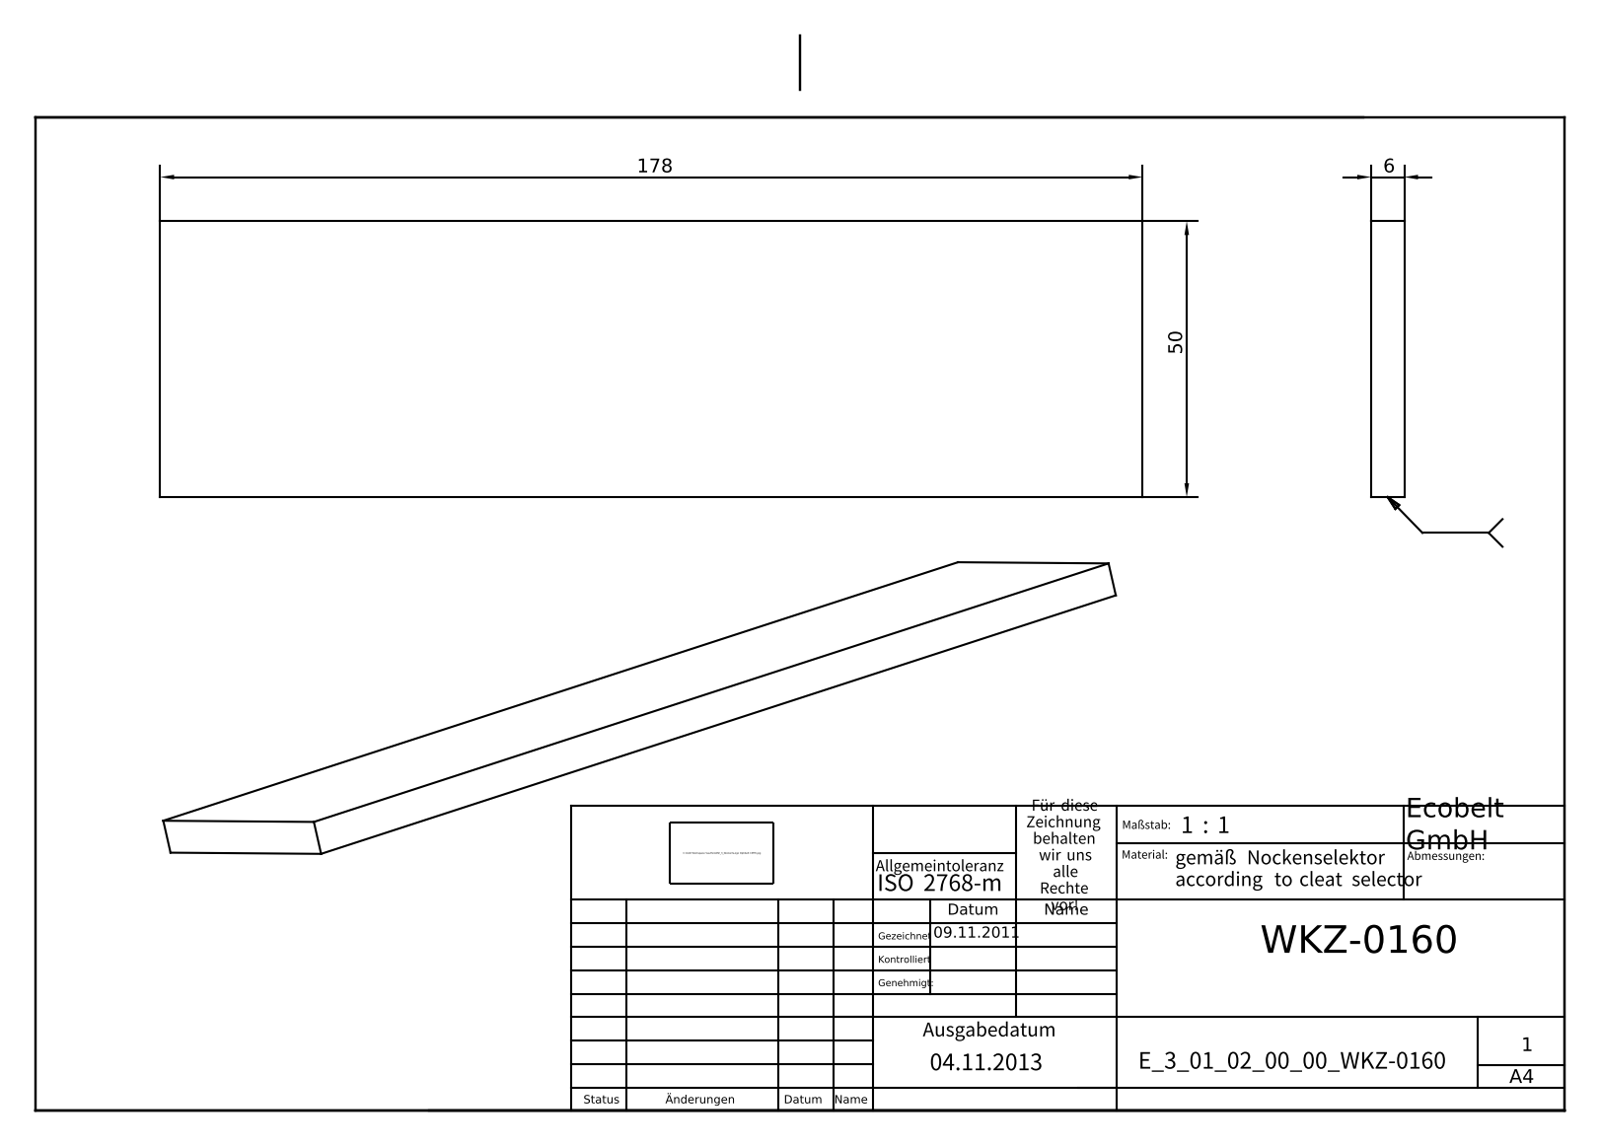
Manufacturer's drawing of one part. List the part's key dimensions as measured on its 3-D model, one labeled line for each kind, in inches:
Part name (STEP PRODUCT): E_3_01_02_00_00_WKZ-0160
STEP written by: Autodesk Inventor 2021 (AUTOMOTIVE_DESIGN)
Units: inches
Bodies: 1 solid, 6 faces (6 planar, 0 cylindrical, 0 other)
Overall size (bounding box): 7.008 × 1.969 × 0.236
Volume: 3.259 in³ · Surface area: 31.83 in²
Main face-to-face distances: 0.236, 1.969, 7.008
